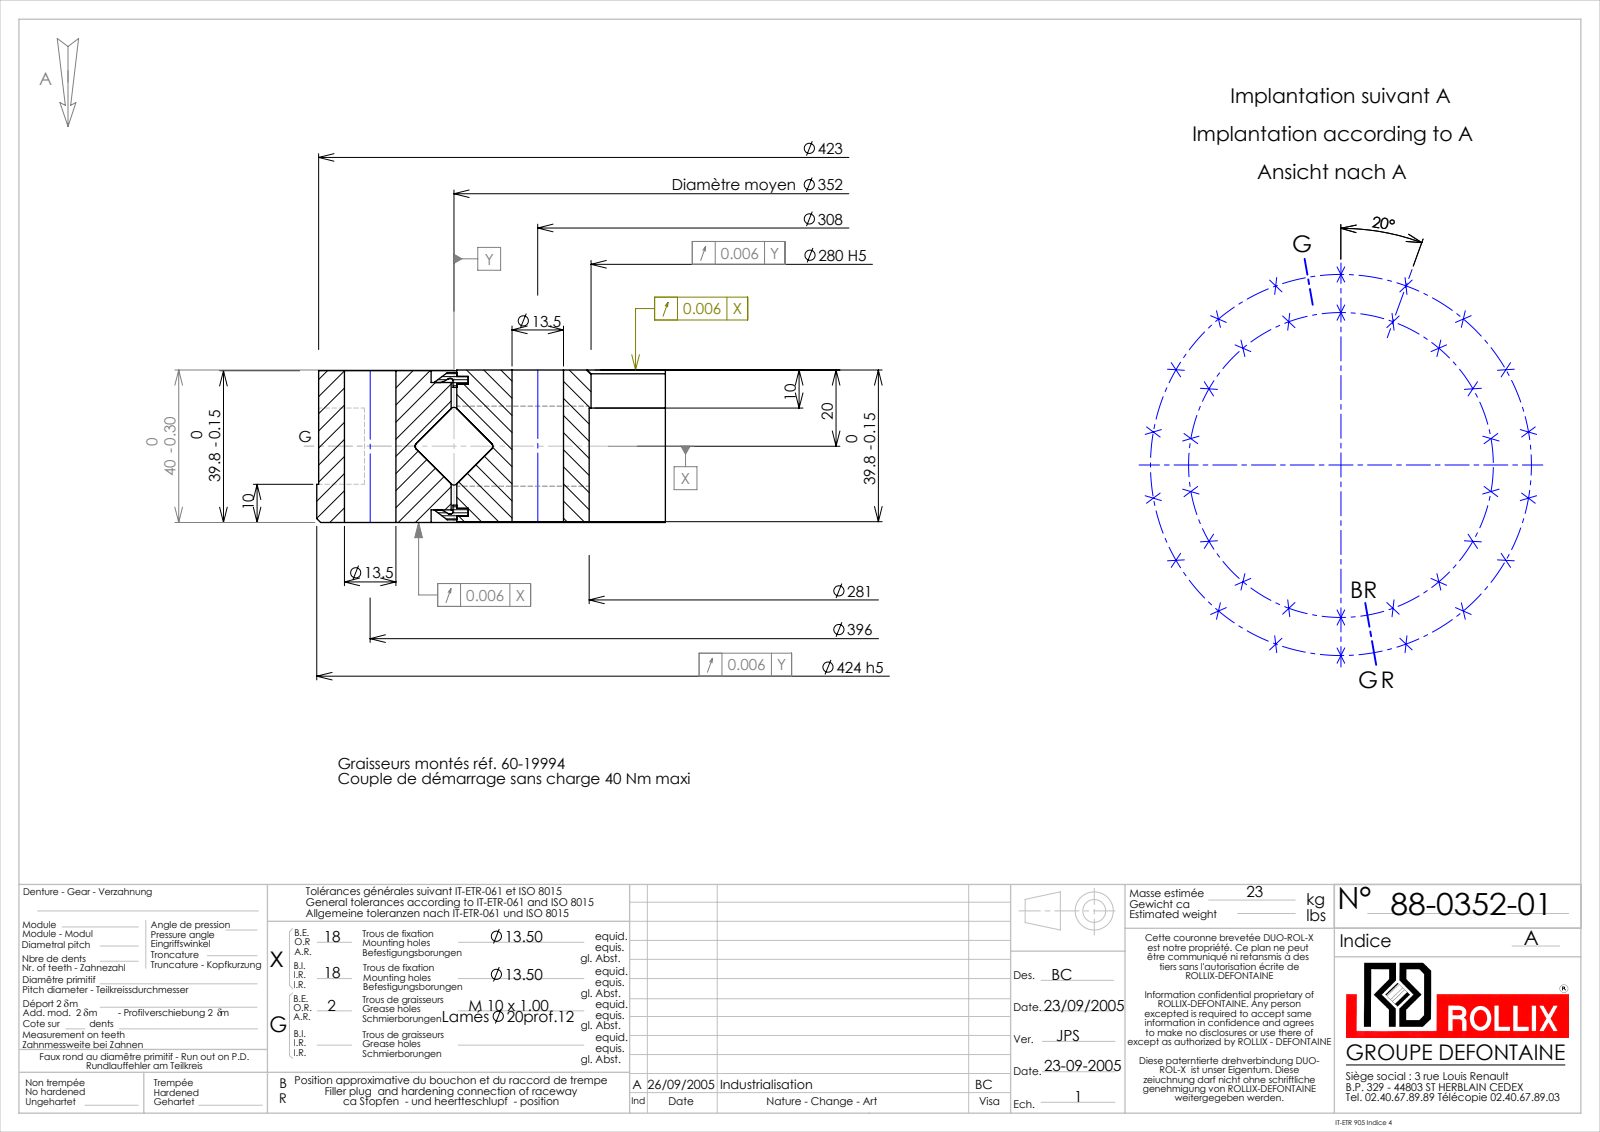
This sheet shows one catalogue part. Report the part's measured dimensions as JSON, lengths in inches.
{"part_name": "88-0352-01", "step_written_by": "SolidWorks 2016 (CONFIG_CONTROL_DESIGN)", "units": "inches", "bodies": {"solids": 7, "faces": 231, "planar": 46, "cylindrical": 130, "other": 55}, "overall_size": [16.693, 16.693, 1.575], "volume_in3": 160.5, "surface_area_in2": 730.5, "round_holes": [[0.531, 36], [0.354, 2], [0.787, 2], [11.024, 1], [11.063, 1], [13.563, 1], [13.799, 1], [13.917, 1], [14.331, 1]], "round_bosses_or_shafts": [[0.394, 2], [16.693, 1], [16.654, 1], [13.878, 1], [0.591, 1]], "face_to_face_distances": [1.567, 1.575, 1.559, 1.437, 0.13, 0.122, 1.445, 0.059, 0.138, 1.516], "hole_center_spacings": [7.795, 12.033, 5.011, 6.063, 5.332, 9.006, 13.036, 11.943]}
